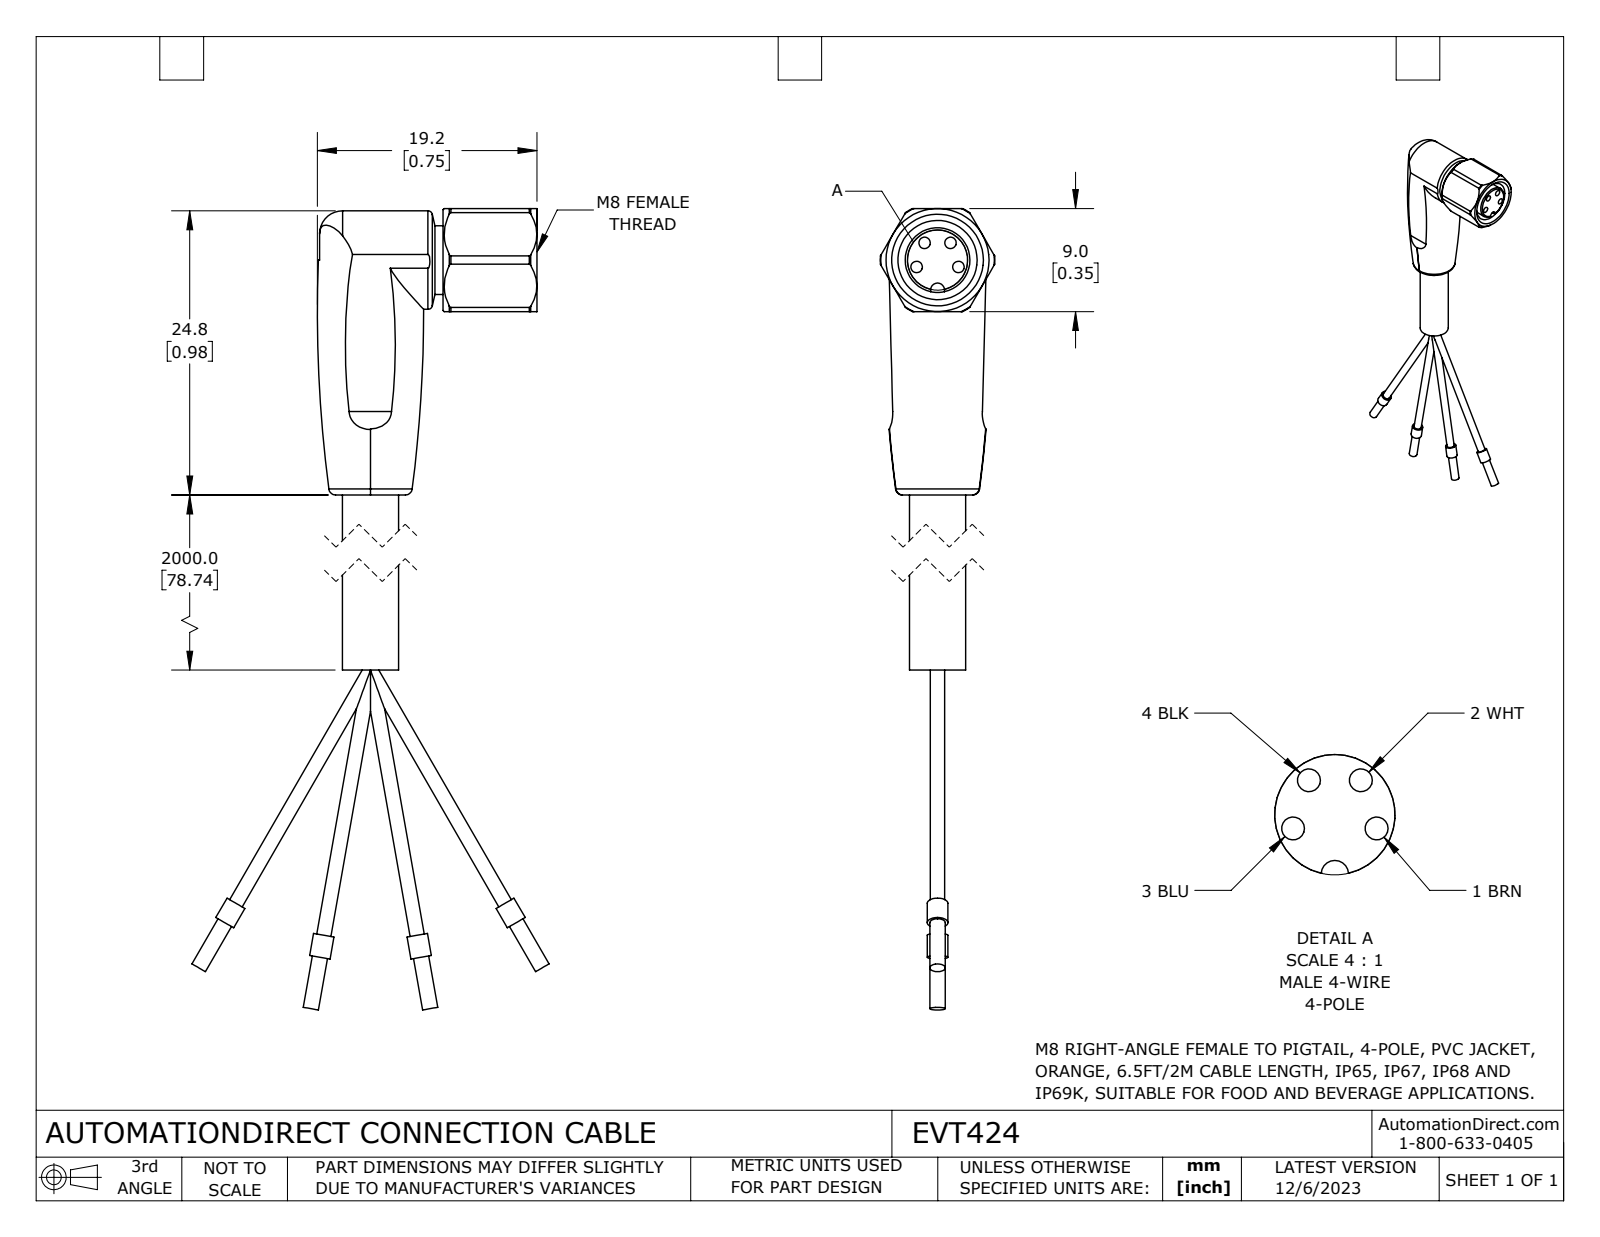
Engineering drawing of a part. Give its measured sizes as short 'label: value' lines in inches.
name: EVT424
written by: SolidWorks 2023 (CONFIG_CONTROL_DESIGN)
unit: in
bodies: 1 solid, 122 faces (37 planar, 53 cylindrical, 32 other)
size: 2.684 × 1.227 × 0.394
volume: 0.147 in³; area: 3.26 in²
holes: 4× ⌀0.039, 1× ⌀0.272
bosses: 4× ⌀0.071, 4× ⌀0.053, 4× ⌀0.049, 1× ⌀0.339, 1× ⌀0.236, 1× ⌀0.222, 1× ⌀0.193
rounds: 2× R0.126, 1× R0.024, 1× R0.197
face distances: 0.354, 0.323, 1.161, 1.516, 0.098, 0.224, 0.531, 0.63, 0.984, 0.077
hole spacings: 0.074, 0.076, 0.087, 0.143, 0.089, 0.143
